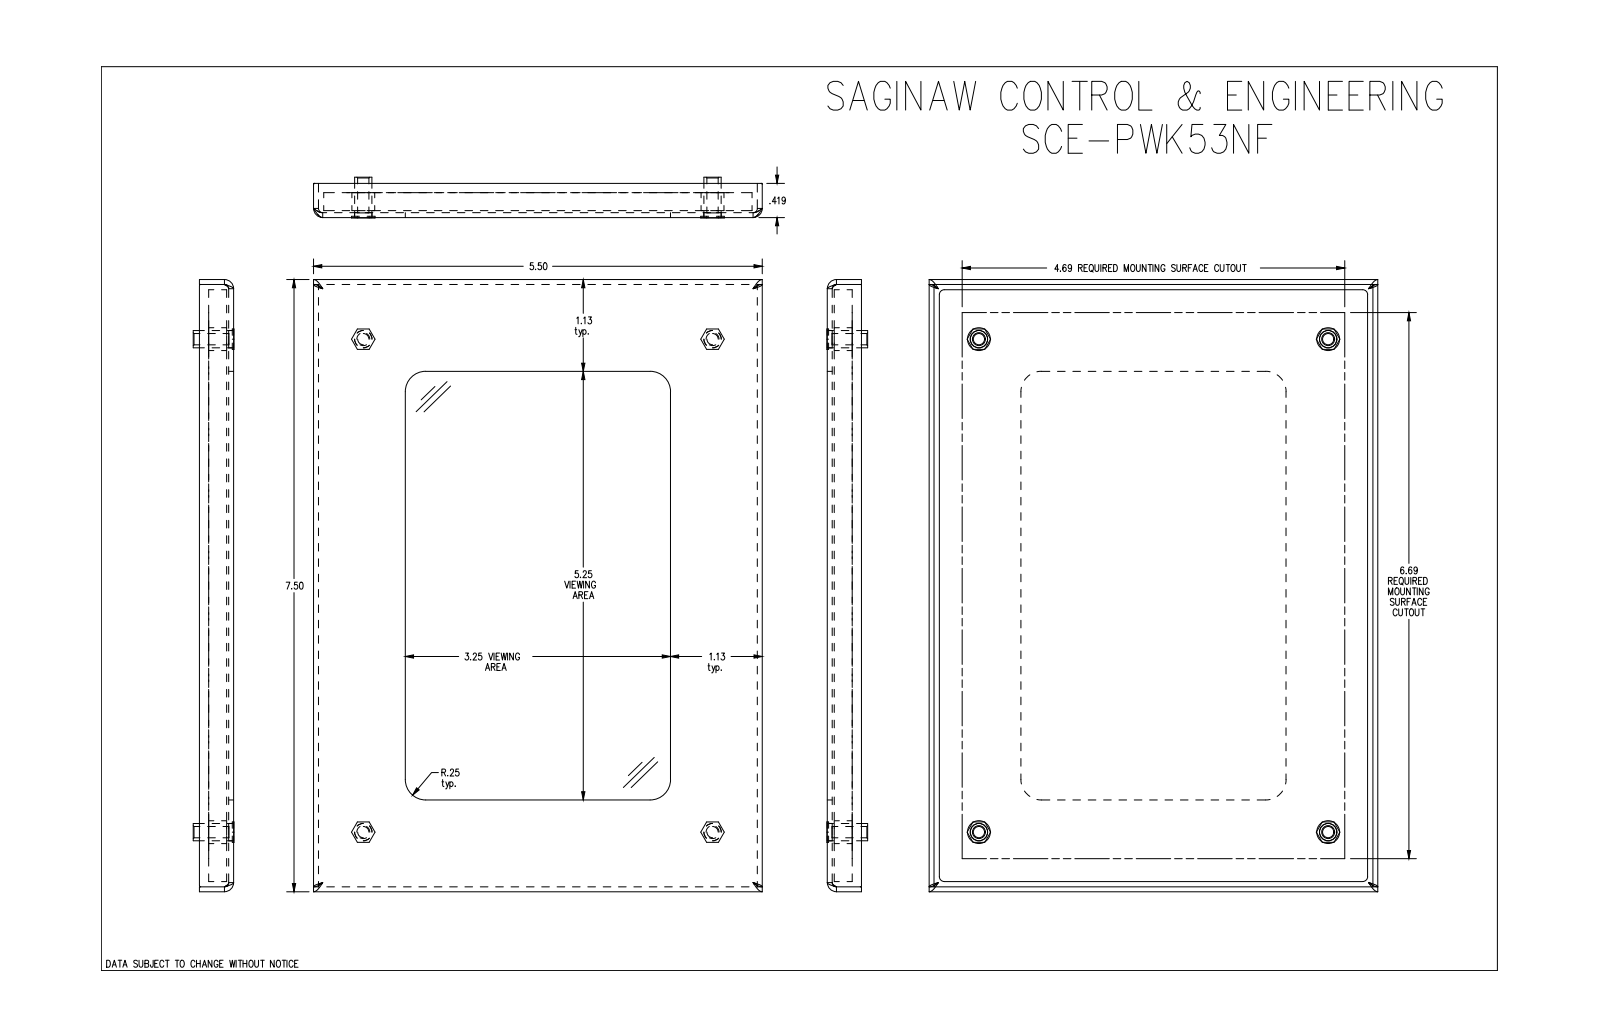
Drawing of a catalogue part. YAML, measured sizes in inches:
part_name: "SCE-PWK53NF"
step_written_by: "SolidWorks 2021 (AUTOMOTIVE_DESIGN)"
units: inches
bodies: {solids: 6, faces: 109, planar: 61, cylindrical: 40, other: 8}
overall_size: [7.5, 5.511, 0.5]
volume: 10.91
surface_area: 153.3
round_holes:
  - {diameter: 0.138, count: 4}
  - {diameter: 0.213, count: 4}
  - {diameter: 0.28, count: 4}
round_bosses_or_shafts:
  - {diameter: 0.212, count: 4}
partial_cylinders:
  - {radius: 0.06, count: 4}
  - {radius: 0.112, count: 4}
  - {radius: 0.25, count: 4}
face_to_face_distances: [0.236, 0.06, 0.261, 0.025, 0.321, 0.085, 5.451, 7.44, 5.391, 0.065]
hole_center_spacings: [6.039, 7.403, 4.276, 4.281, 4.281, 4.286, 7.4, 7.406]
